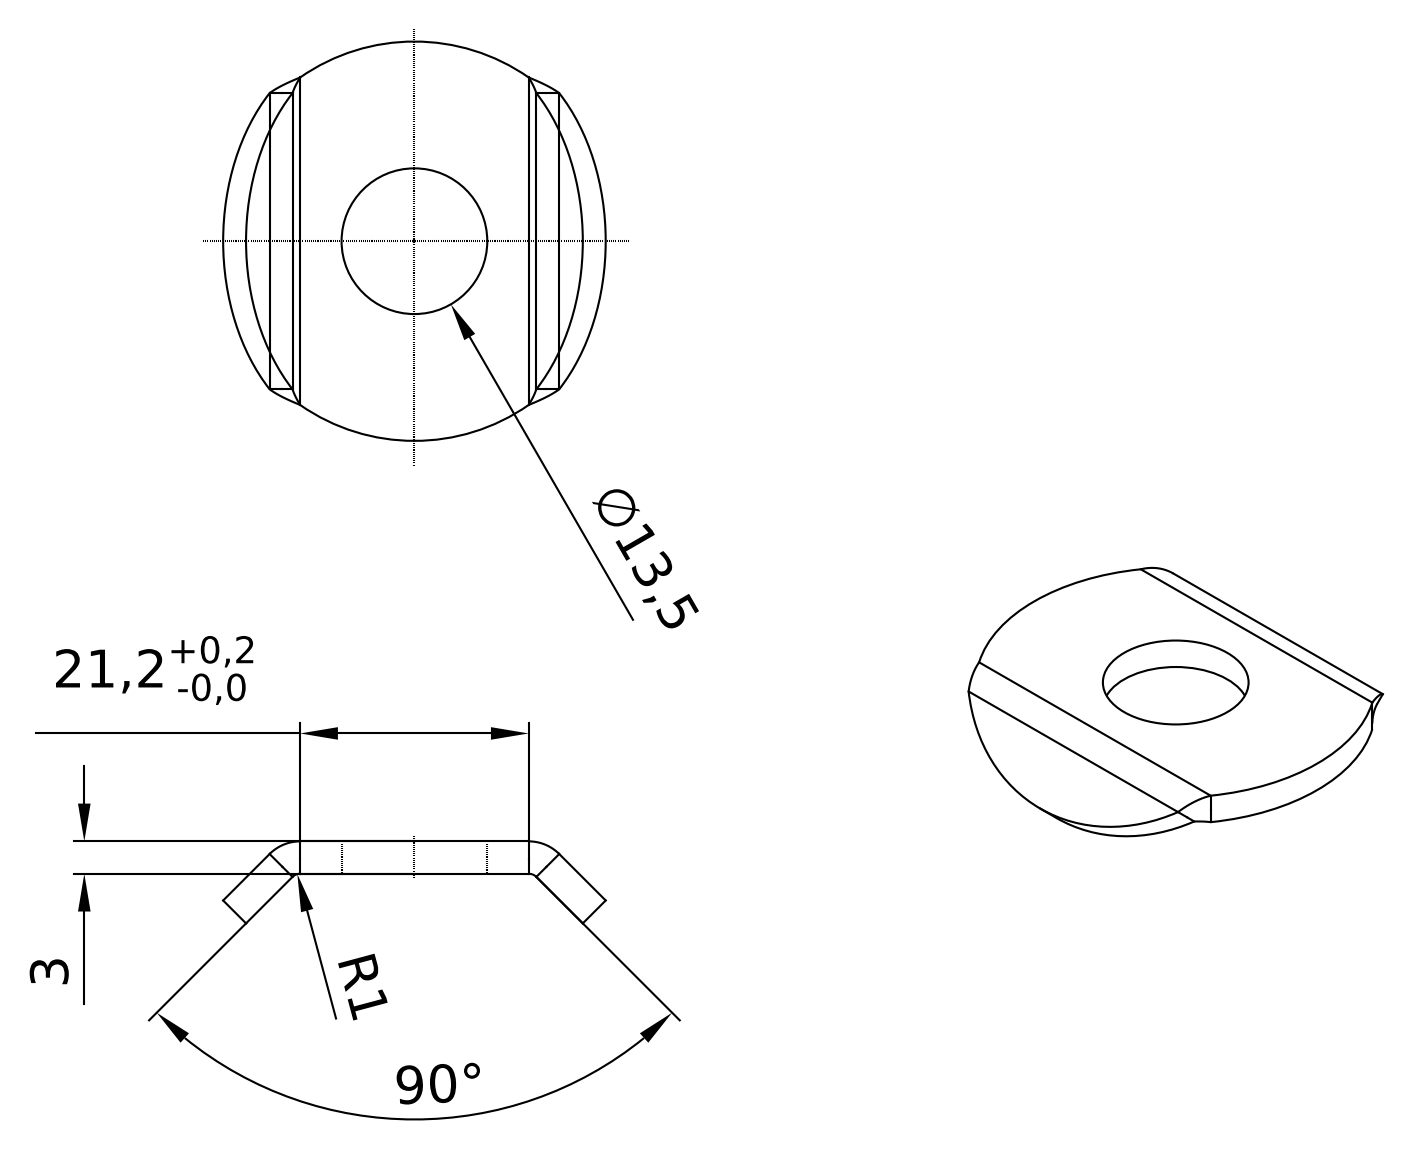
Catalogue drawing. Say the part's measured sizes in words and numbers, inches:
The part is named "800 116-E1". Its 3-D file was written by "Autodesk Inventor 8 (AUTOMOTIVE_DESIGN)". It is 1 solid with 22 faces: 6 planar, 12 cylindrical and 4 other. Overall it measures 1.457 by 0.987 by 0.987 inches. Its volume is 0.172 cubic inches and its surface area 3.655 square inches. Round holes: 1 of diameter 0.531. Partial cylindrical surfaces (rounded edges, fillets, slot ends): 3 of radius 0.728, 2 of radius 0.039, 2 of radius 0.157. The main face-to-face distances are 0.118.
